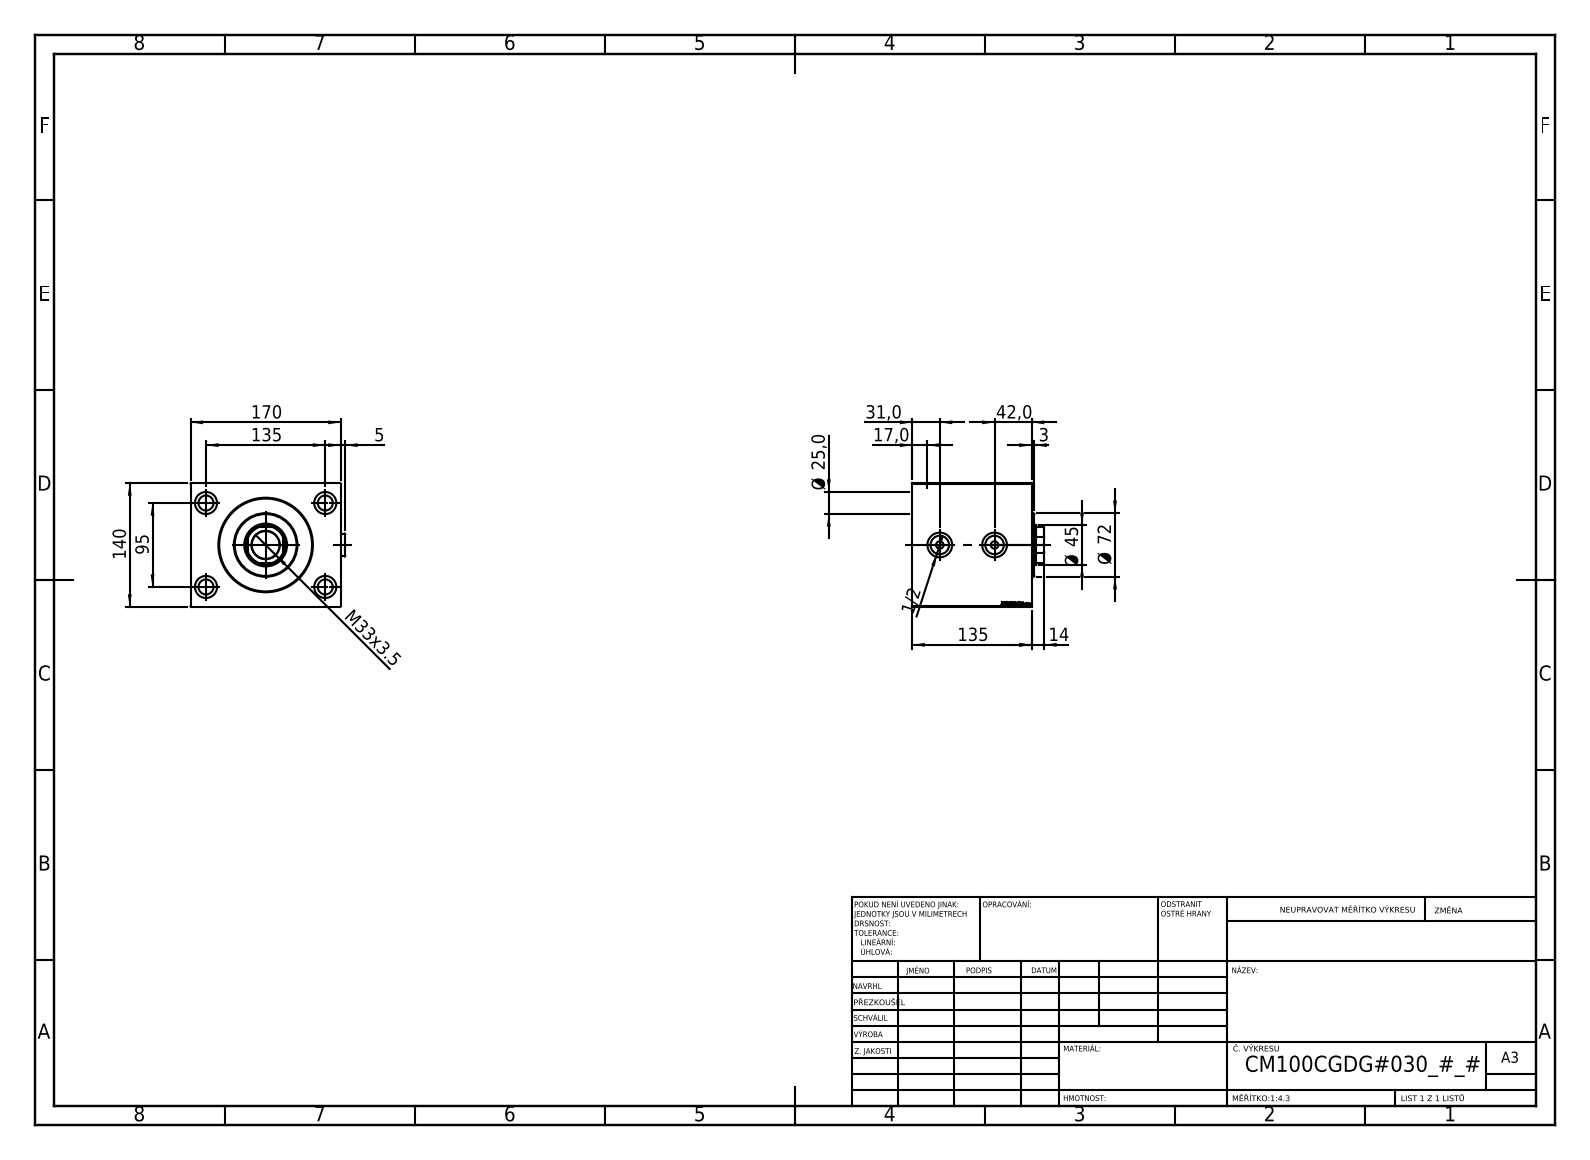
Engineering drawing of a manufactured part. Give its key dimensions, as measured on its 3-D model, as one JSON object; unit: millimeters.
{"part_name": "Zatka_OIL_PORT; V450CM_C_VCP; V450CM_VC_B; V450CM_C_Body", "step_written_by": "SolidWorks 2019 (CONFIG_CONTROL_DESIGN)", "units": "millimeters", "bodies": {"solids": 5, "faces": 917, "planar": 443, "cylindrical": 76, "other": 398}, "overall_size": [174.9, 149, 140], "volume_mm3": 2963000, "surface_area_mm2": 246105, "round_holes": [[17, 4], [25, 4], [8.5, 2], [20.96, 2], [28, 2], [31.5, 1], [45, 1], [48.5, 1], [100, 1], [102, 1], [105, 1]], "round_bosses_or_shafts": [[26, 2], [72, 1]], "partial_cylinders_radius": [[22, 1]], "face_to_face_distances": [140, 170, 135, 51, 84, 21.6, 29.4, 113.4, 10, 31.6], "hole_center_spacings": [82.54, 95, 135, 165.08, 62]}
